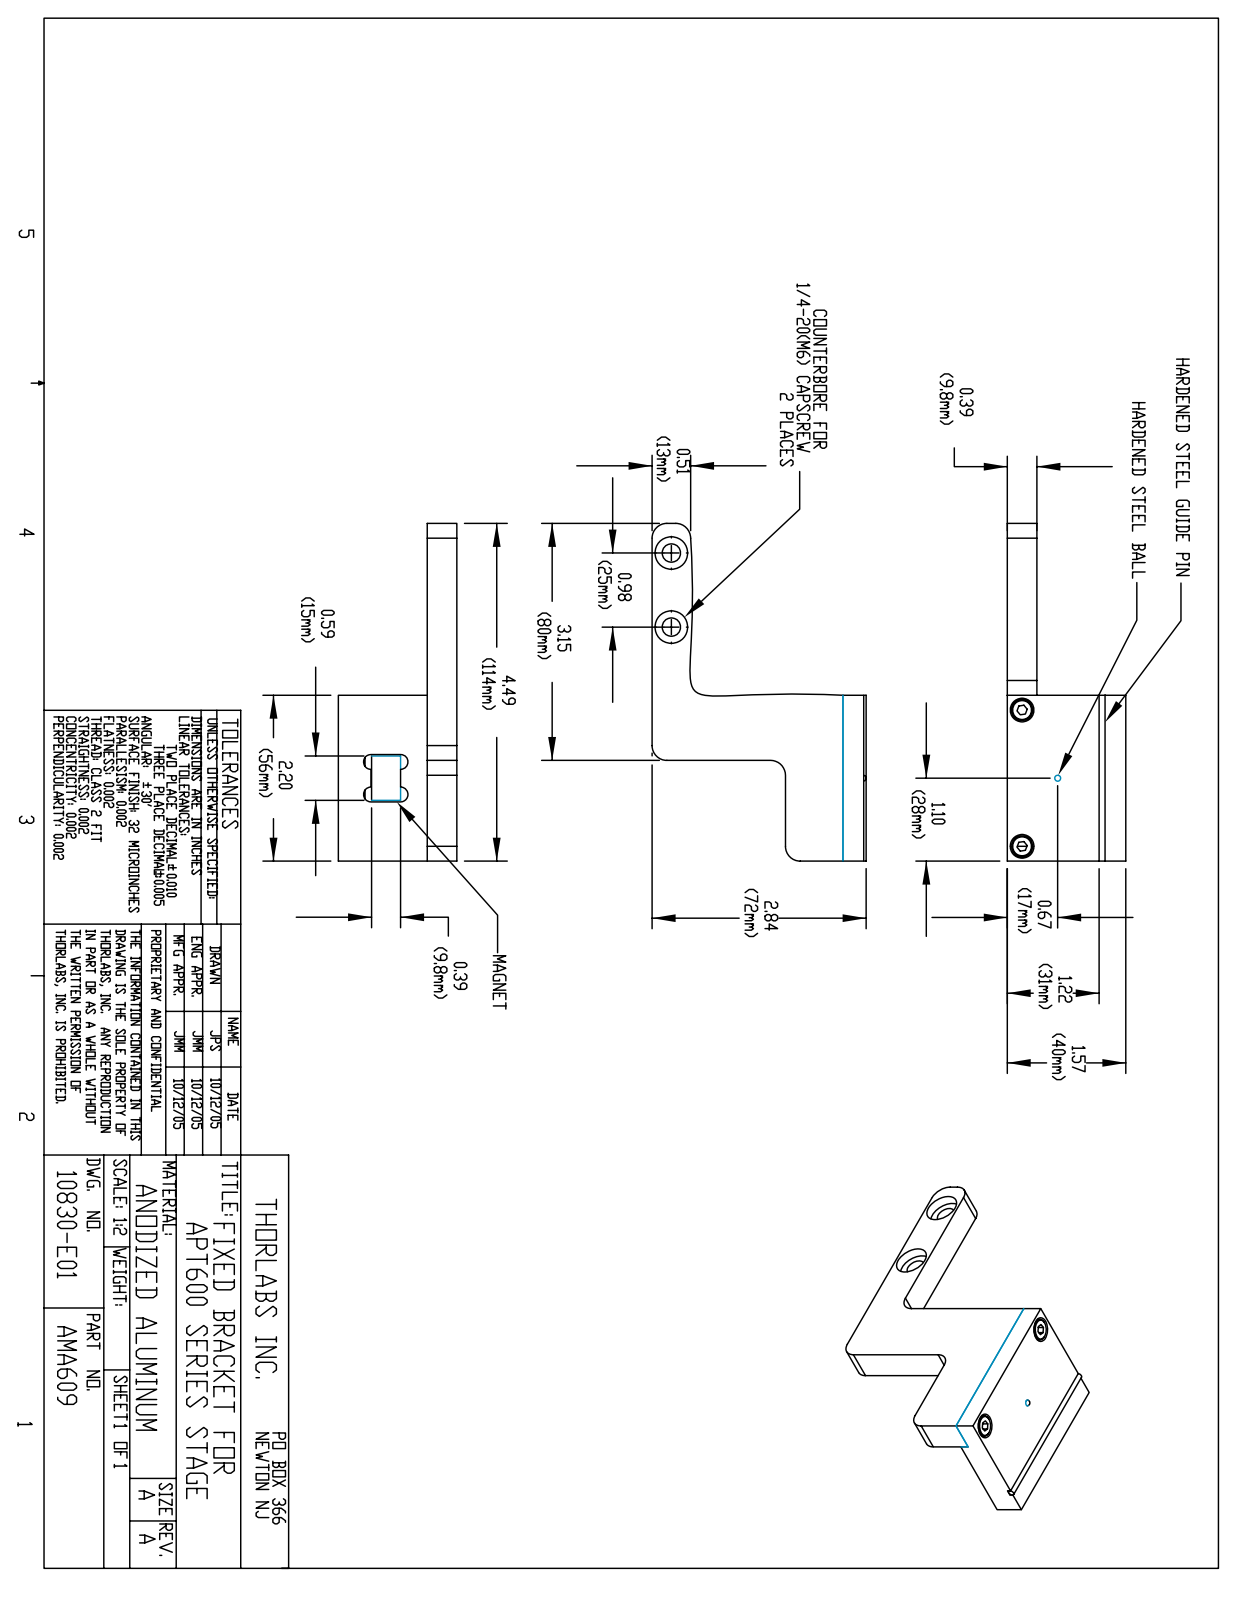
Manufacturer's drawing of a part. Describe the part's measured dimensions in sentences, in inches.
The part is named "10830-E0W". Its 3-D file was written by "SolidWorks 2007 (AUTOMOTIVE_DESIGN)". It is 0 solids with 85 faces: 45 planar, 34 cylindrical and 6 other. Overall it measures 4.488 by 2.843 by 1.575 inches. Round holes: 2 of diameter 0.244, 2 of diameter 0.315, 2 of diameter 0.433. Round bosses or shafts: 2 of diameter 0.276, 1 of diameter 0.079. Partial cylindrical surfaces (rounded edges, fillets, slot ends): 6 of radius 0.197, 4 of radius 0.098. The main face-to-face distances are 0.394, 2.417, 2.811, 1.181, 1.575, 2.205, 0.512, 1.906, 2.299, 0.866. The hole center spacings are 0.984, 1.811.
